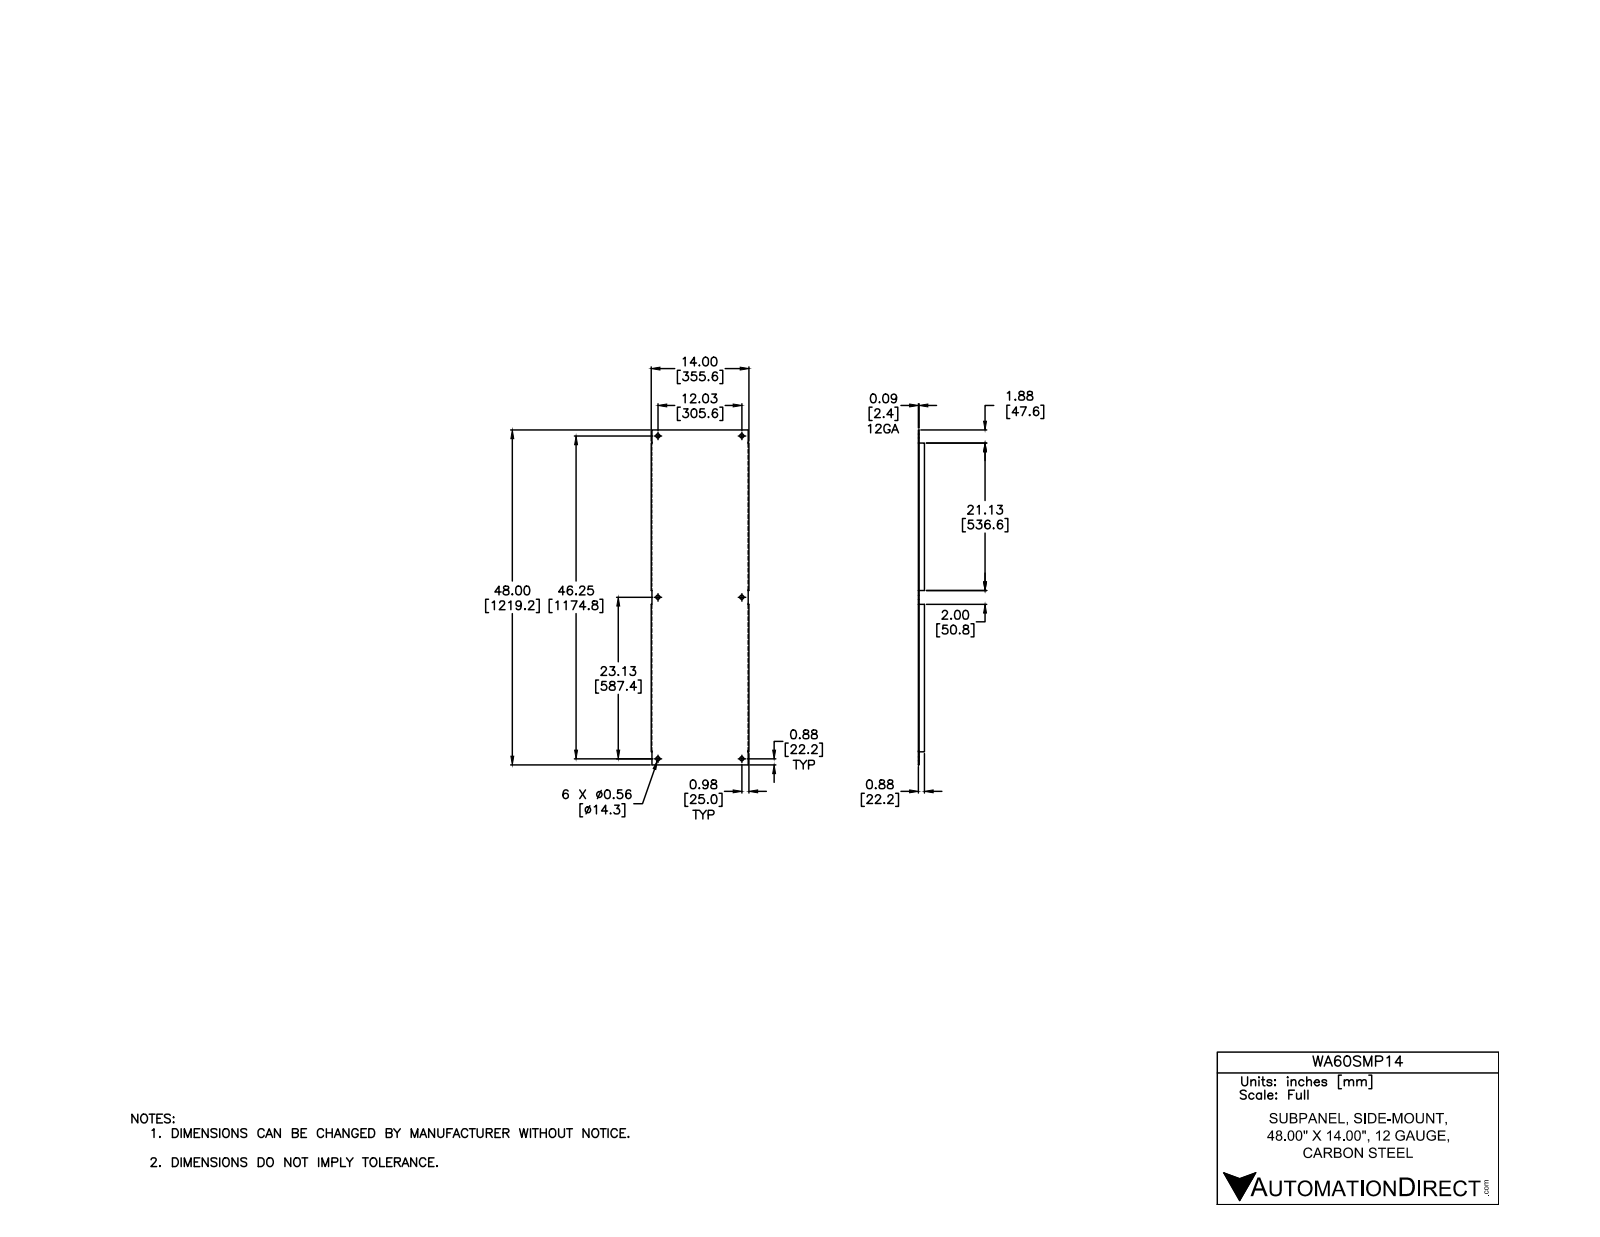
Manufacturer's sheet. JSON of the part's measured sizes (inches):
{"part_name": "WA60SMP14-WA90SMP20", "step_written_by": "Autodesk Inventor 2012 (AUTOMOTIVE_DESIGN)", "units": "inches", "bodies": {"solids": 1, "faces": 48, "planar": 34, "cylindrical": 14, "other": 0}, "overall_size": [48, 14, 0.875], "volume_in3": 68.72, "surface_area_in2": 1479, "round_holes": [[0.563, 6]], "partial_cylinders_radius": [[0.015, 2], [0.109, 2]], "face_to_face_distances": [0.094, 13.906, 13.813, 14, 0.781, 0.875, 48, 0.109, 13.891, 0.015], "hole_center_spacings": [12.032, 23.125, 23.125, 26.068, 26.068, 46.25, 47.789]}
